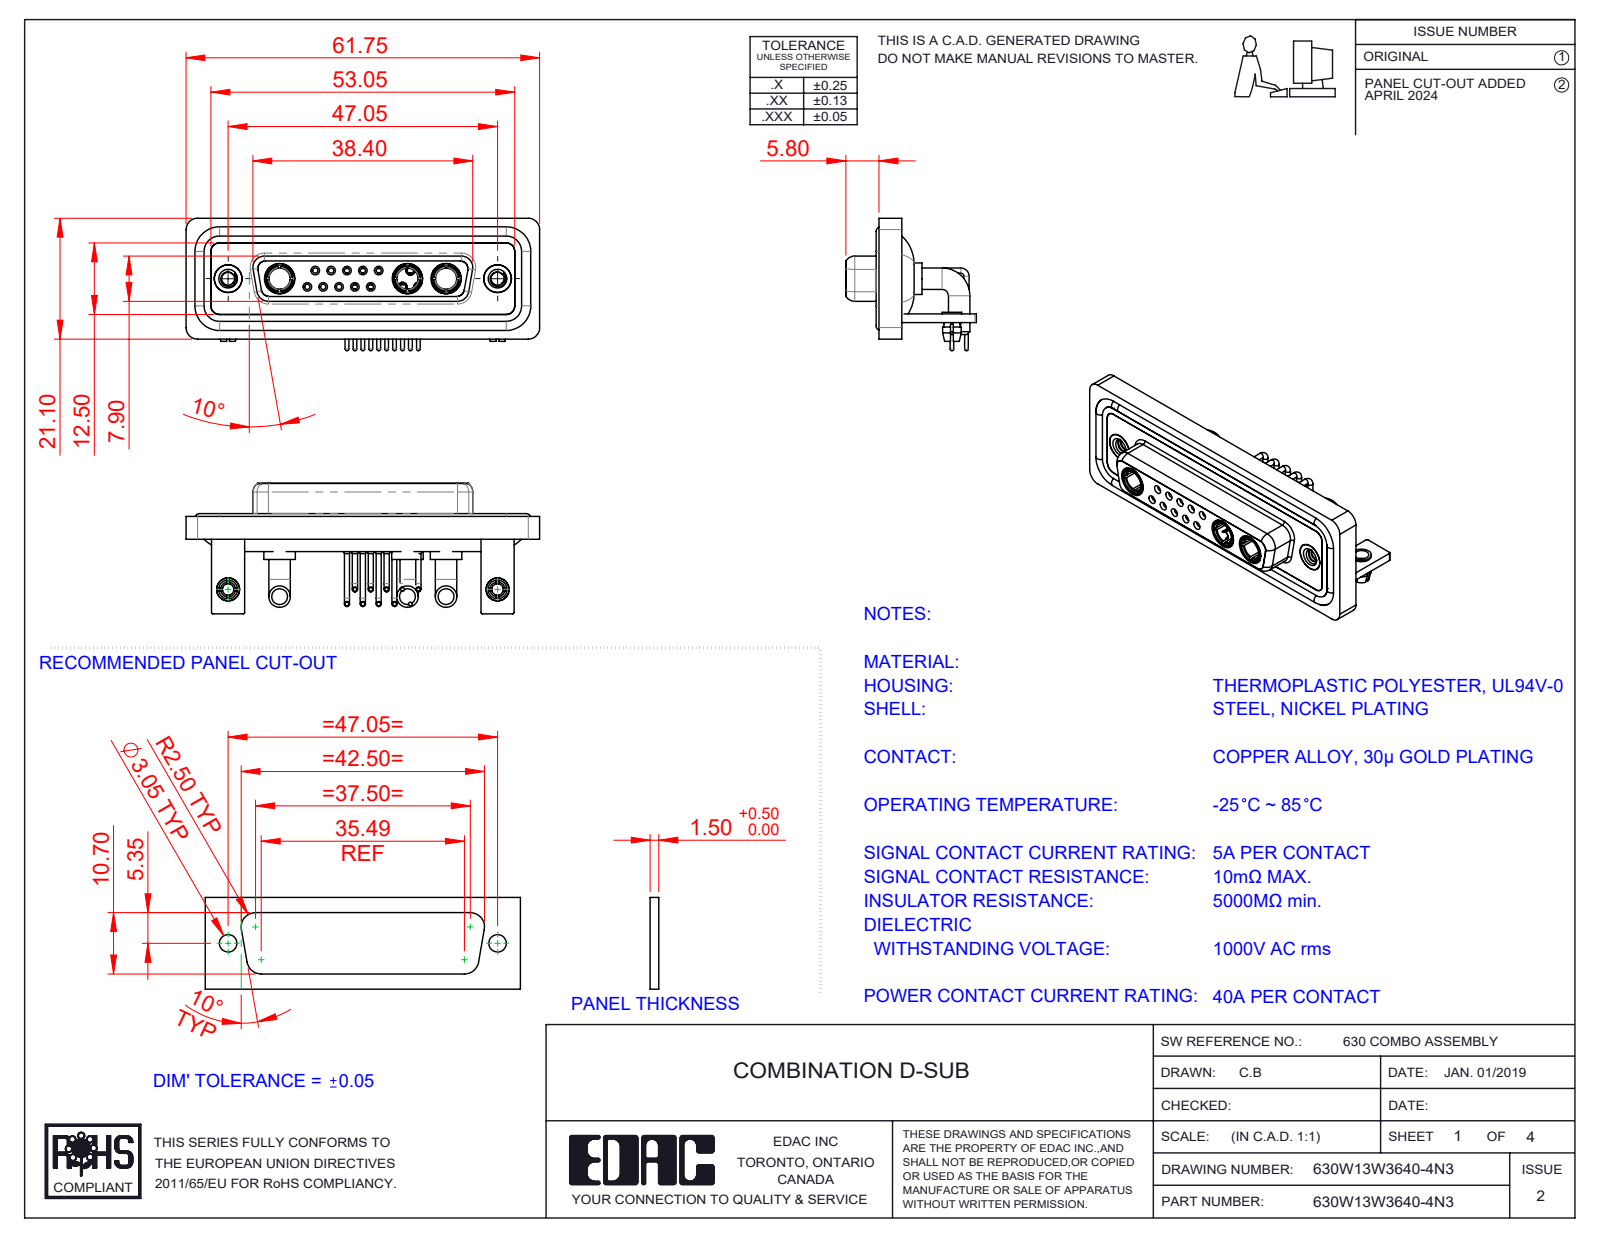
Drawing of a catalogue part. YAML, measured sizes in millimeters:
part_name: "630Combo Stabilizer Bracket_50 Contacts; 630Combo Waterproof Housing_25 Contacts; 630Combo Board Lock_50 Contacts; 630Combo Shell Rear_25 Contacts (+7 more)"
step_written_by: "SolidWorks 2023 (CONFIG_CONTROL_DESIGN)"
units: millimeters
bodies: {solids: 27, faces: 1290, planar: 410, cylindrical: 549, other: 331}
overall_size: [61.75, 23.12, 22.8]
volume: 9091
surface_area: 15373
round_holes:
  - {diameter: 2, count: 12}
  - {diameter: 0.9, count: 10}
  - {diameter: 1.1, count: 10}
  - {diameter: 1.5, count: 10}
  - {diameter: 1.6, count: 5}
  - {diameter: 1.7, count: 5}
  - {diameter: 4.85, count: 5}
  - {diameter: 3.7, count: 3}
  - {diameter: 5.3, count: 3}
  - {diameter: 2.26, count: 2}
  - {diameter: 2.5, count: 2}
  - {diameter: 3.2, count: 2}
round_bosses_or_shafts:
  - {diameter: 0.9, count: 15}
  - {diameter: 1.6, count: 12}
  - {diameter: 0.65, count: 10}
  - {diameter: 3.75, count: 6}
  - {diameter: 2, count: 5}
  - {diameter: 1.5, count: 5}
  - {diameter: 5.5, count: 3}
  - {diameter: 5.2, count: 3}
partial_cylinders:
  - {radius: 2, count: 19}
  - {radius: 1.5, count: 18}
  - {radius: 0.25, count: 16}
  - {radius: 1.35, count: 8}
  - {radius: 1.6, count: 8}
  - {radius: 0.5, count: 5}
  - {radius: 0.6, count: 4}
  - {radius: 0.65, count: 4}
face_to_face_distances: [0.4, 1.8, 2.9, 3.7, 1.5, 4.1, 1.1, 1.4, 1.6, 3.1]
hole_center_spacings: [3.16, 2.77, 5.54, 5.04, 8.31, 5.03, 7.49, 11.08]
